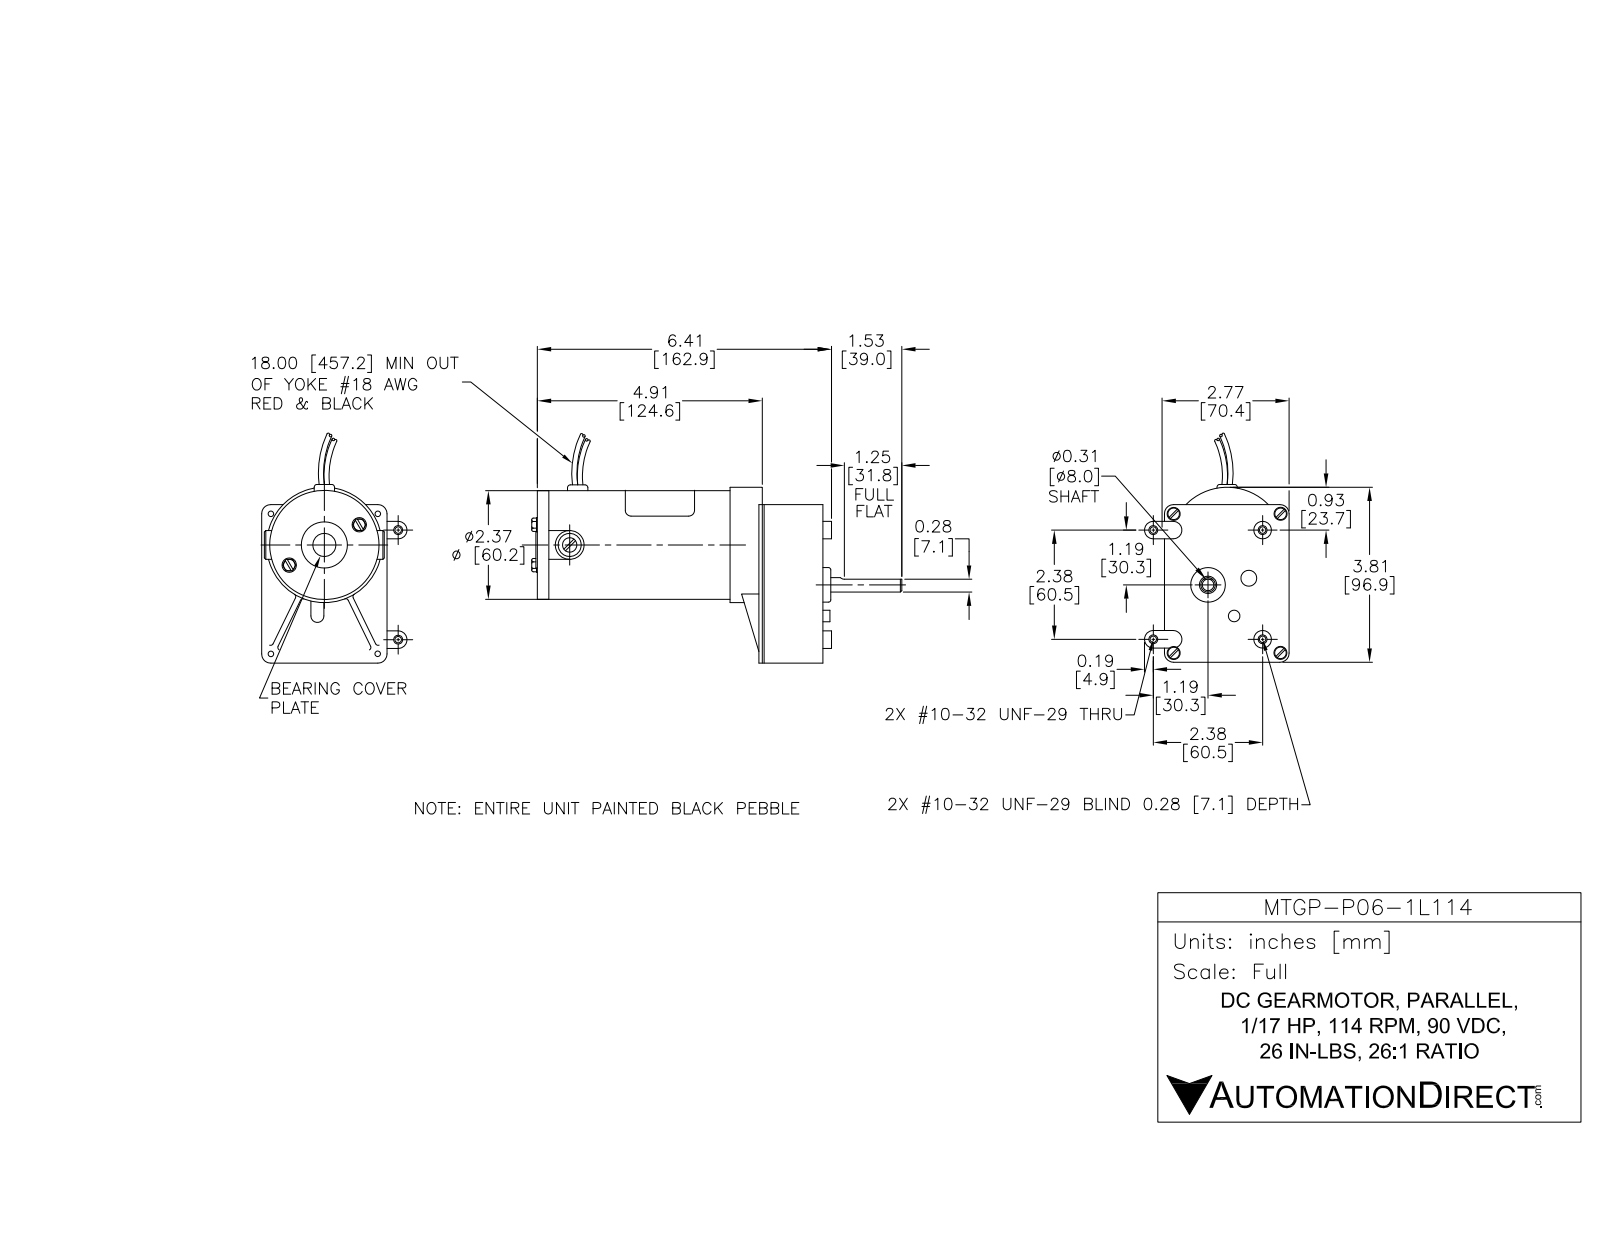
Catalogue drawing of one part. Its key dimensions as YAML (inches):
part_name: "MTGP-P06-1L114"
step_written_by: "SolidWorks 2016 (AUTOMOTIVE_DESIGN)"
units: inches
bodies: {solids: 27, faces: 266, planar: 115, cylindrical: 130, other: 21}
overall_size: [7.922, 5.092, 3.181]
volume: 20.18
surface_area: 156.4
round_holes:
  - {diameter: 0.194, count: 5}
  - {diameter: 0.063, count: 4}
  - {diameter: 0.283, count: 4}
  - {diameter: 0.156, count: 2}
  - {diameter: 0.25, count: 1}
  - {diameter: 0.312, count: 1}
  - {diameter: 0.562, count: 1}
  - {diameter: 1, count: 1}
  - {diameter: 2.25, count: 1}
round_bosses_or_shafts:
  - {diameter: 0.312, count: 4}
  - {diameter: 0.38, count: 2}
  - {diameter: 0.1, count: 2}
  - {diameter: 2.46, count: 1}
  - {diameter: 2.375, count: 1}
  - {diameter: 0.75, count: 1}
  - {diameter: 0.625, count: 1}
  - {diameter: 0.625, count: 1}
partial_cylinders:
  - {radius: 0.031, count: 10}
  - {radius: 0.1, count: 4}
  - {radius: 0.19, count: 4}
  - {radius: 0.25, count: 2}
  - {radius: 0.134, count: 1}
  - {radius: 0.141, count: 1}
  - {radius: 1.222, count: 1}
face_to_face_distances: [1.4, 0.25, 4.833, 6.233, 4.583, 5.983, 4.194, 3.944, 0.639, 2.039]
hole_center_spacings: [1.223, 1.729, 0.373, 0.44, 0.875, 1.306, 1.332, 1.539]
